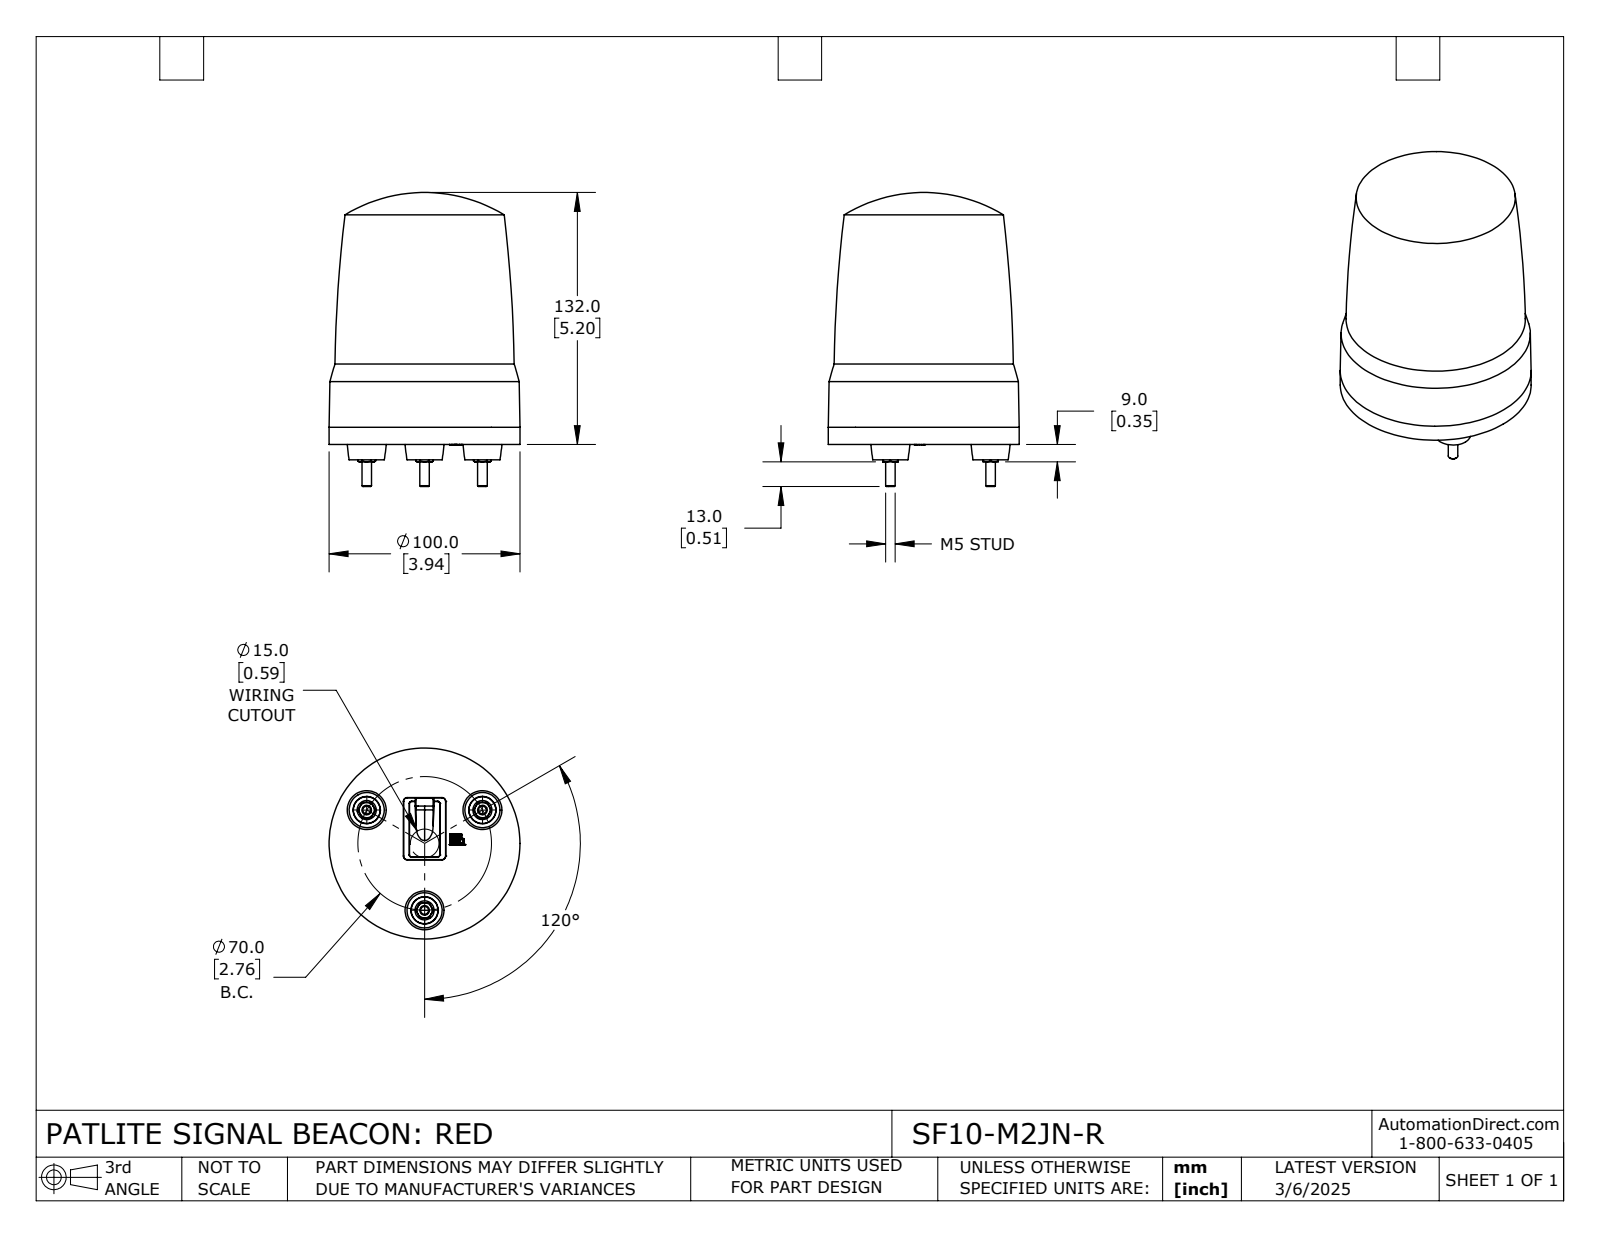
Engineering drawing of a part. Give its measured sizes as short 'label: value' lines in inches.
name: SF10-M2JN-R
written by: SolidWorks 2024 (CONFIG_CONTROL_DESIGN)
unit: in
bodies: 1 solid, 327 faces (159 planar, 14 cylindrical, 154 other)
size: 6.063 × 3.937 × 3.937
volume: 52.48 in³; area: 81.51 in²
bosses: 3× ⌀0.394, 3× ⌀0.197, 1× ⌀3.937
face distances: 0.315, 0.033, 0.348, 0.063, 0.411, 0.096, 0.15, 0.165, 0.199, 0.262
